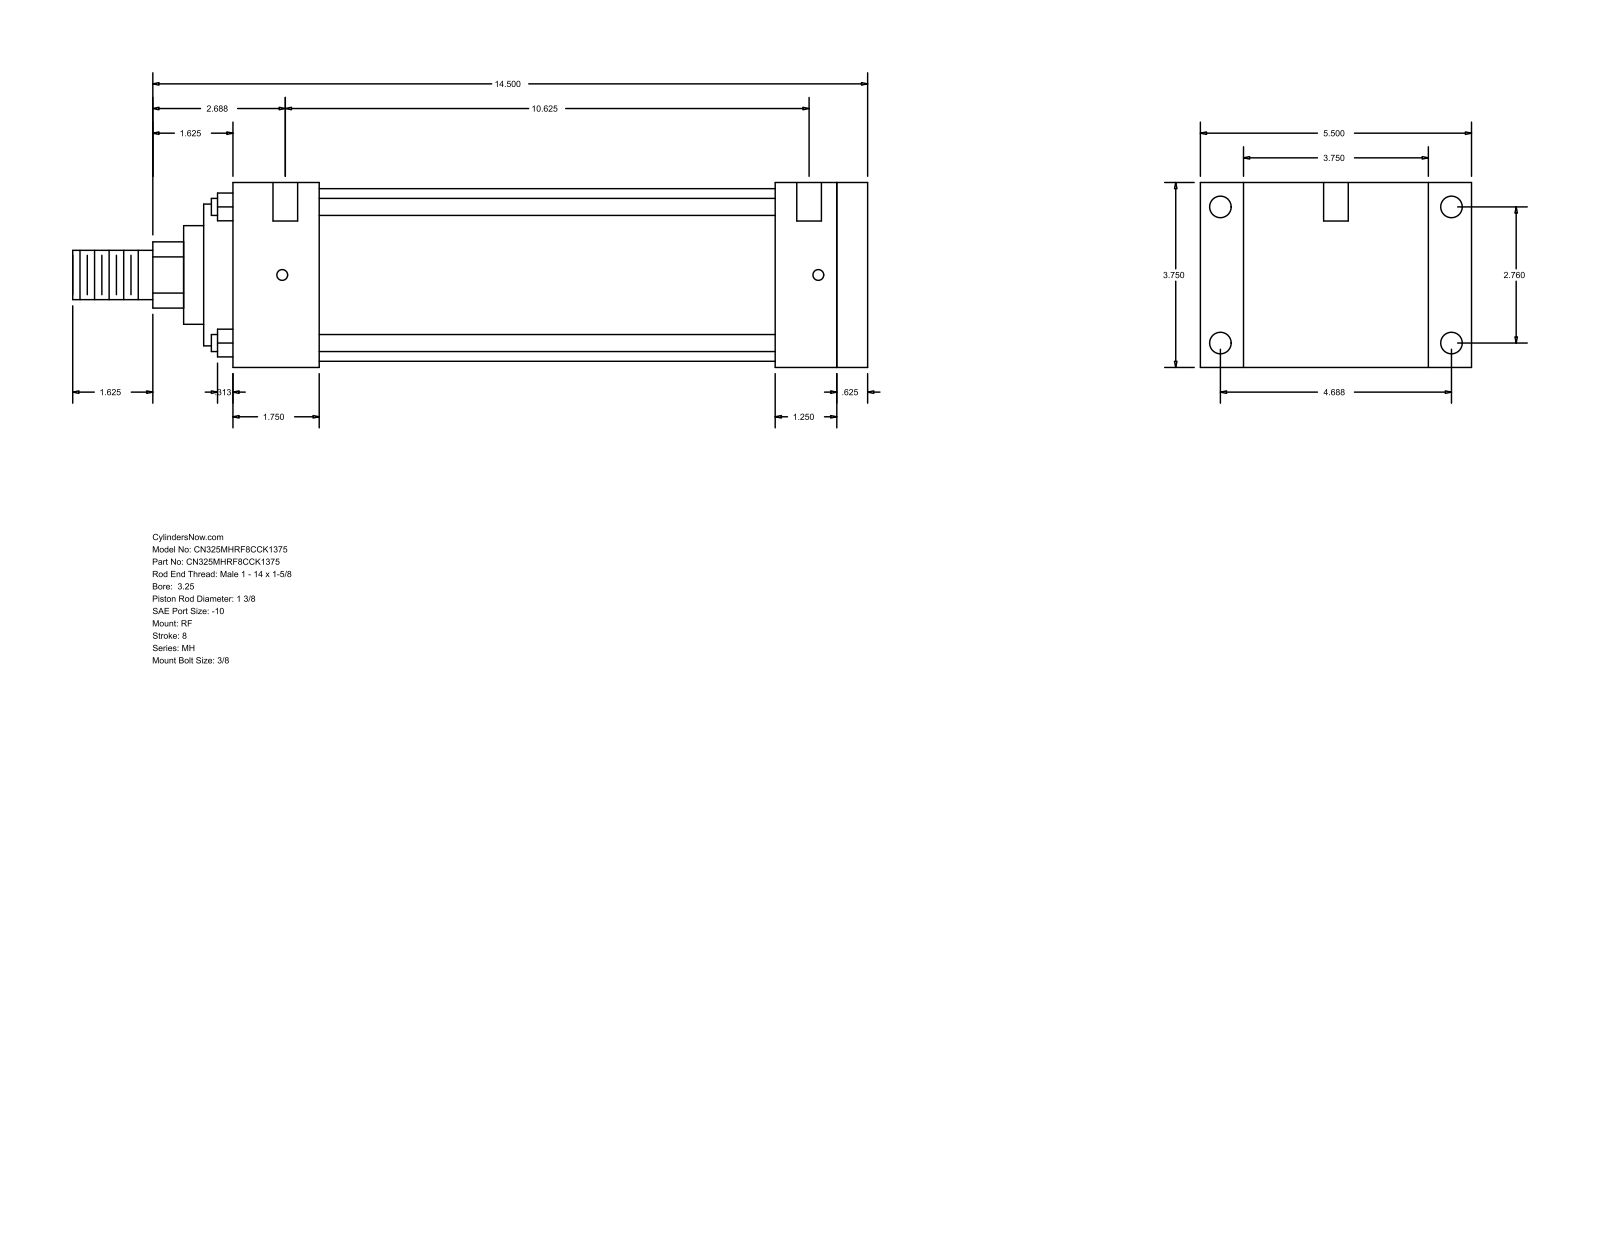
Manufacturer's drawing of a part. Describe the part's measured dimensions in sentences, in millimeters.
The part is named "MH_RF__0325_1.375". Its 3-D file was written by "GSSL Pune (CONFIG_CONTROL_DESIGN)". It is 0 solids with 94 faces: 65 planar, 29 cylindrical and 0 other. Overall it measures 409.57 by 139.7 by 95.25 millimeters. Round holes: 4 of diameter 5.56, 4 of diameter 11.13, 2 of diameter 12.7. Round bosses or shafts: 4 of diameter 8.76, 1 of diameter 88.9, 1 of diameter 73.03, 1 of diameter 50.8, 1 of diameter 34.92, 1 of diameter 25.4. Partial cylindrical surfaces (rounded edges, fillets, slot ends): 1 of radius 17.06. The main face-to-face distances are 95.24, 327.03, 311.16, 15.87, 22.23, 117.47, 44.45, 266.71, 282.58, 279.41. The hole center spacings are 70.1, 119.06, 138.16, 276.23, 1.59, 4.76, 269.88, 271.47.
